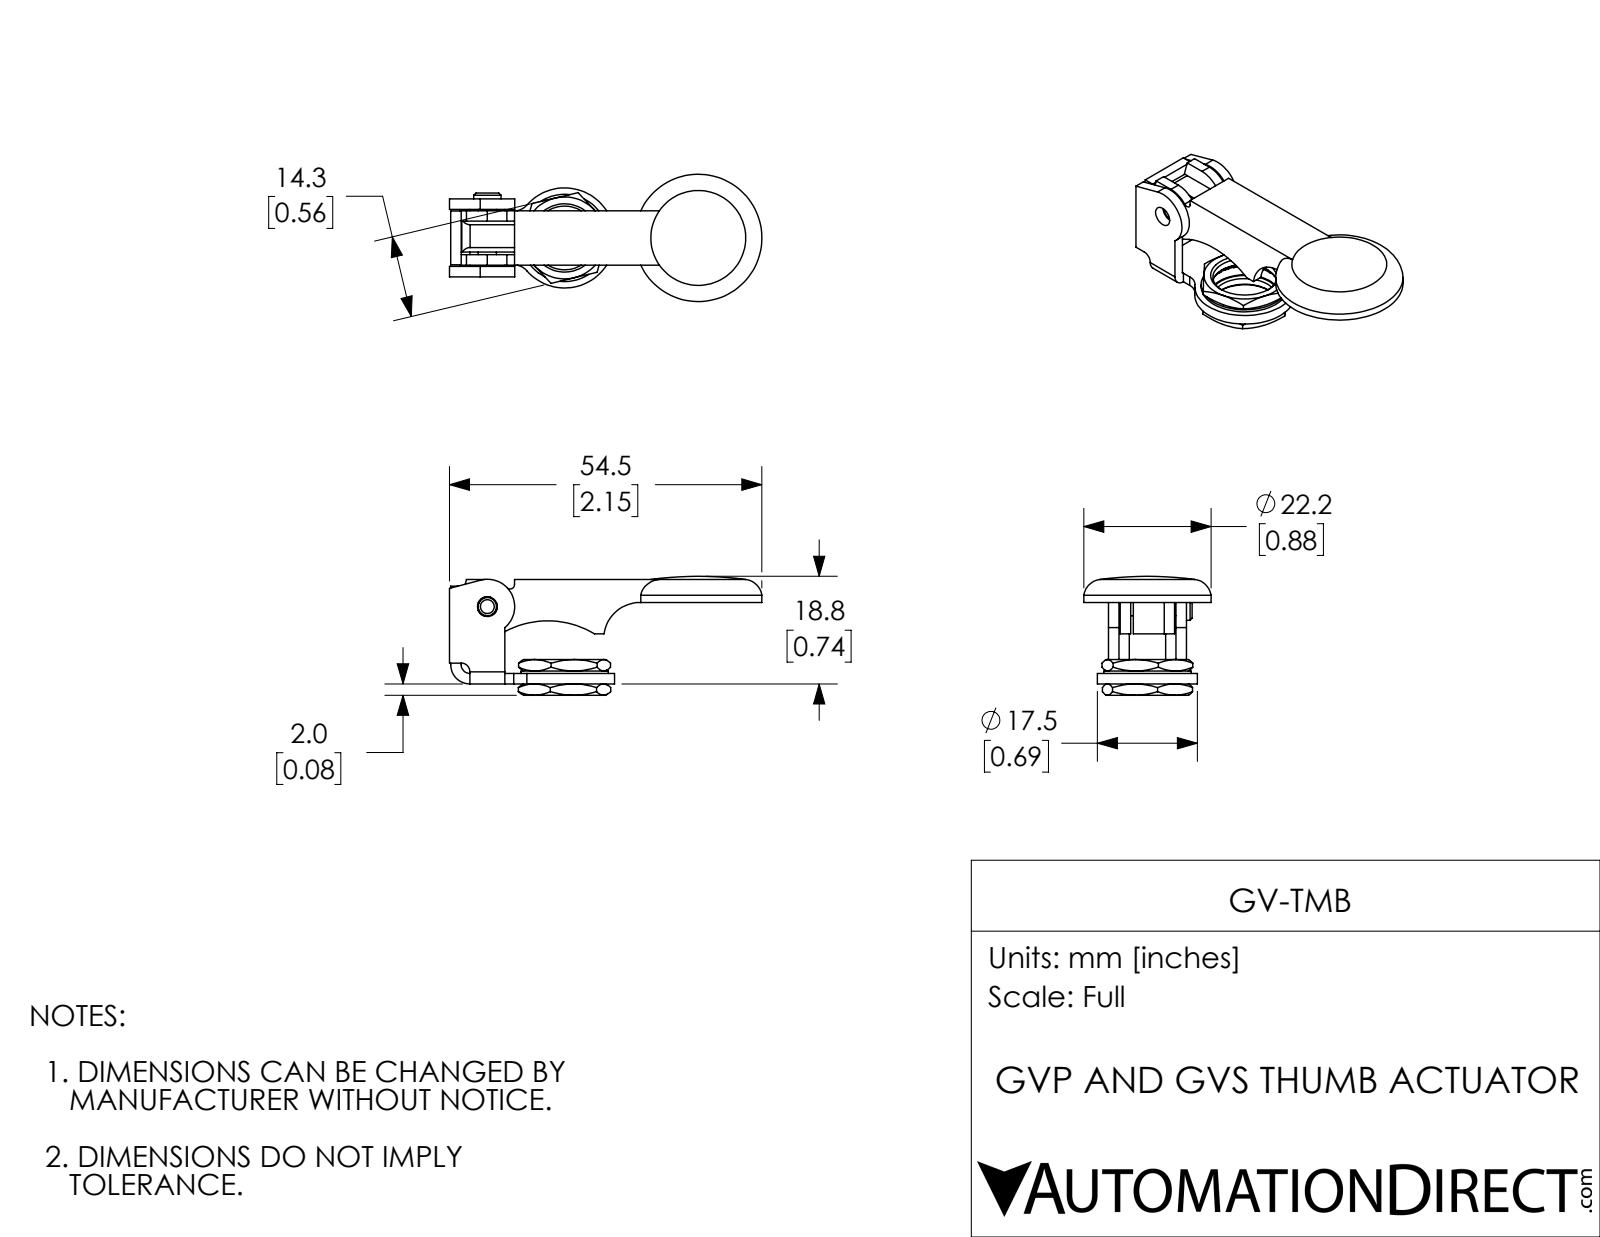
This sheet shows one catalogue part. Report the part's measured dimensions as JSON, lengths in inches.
{"part_name": "GV-TMB", "step_written_by": "SolidWorks 2018 (AUTOMOTIVE_DESIGN)", "units": "inches", "bodies": {"solids": 8, "faces": 304, "planar": 128, "cylindrical": 128, "other": 48}, "overall_size": [2.148, 0.875, 0.817], "volume_in3": 0.259, "surface_area_in2": 8.948, "round_holes": [[0.133, 1], [0.136, 1], [0.438, 1], [0.484, 1], [0.731, 1]], "round_bosses_or_shafts": [[0.875, 1], [0.6, 1], [0.187, 1], [0.125, 1], [0.125, 1], [0.096, 1]], "partial_cylinders_radius": [[0.06, 5], [0.014, 4], [0.011, 2], [0.018, 2], [0.083, 2], [0.12, 2], [0.031, 1], [0.047, 1]], "face_to_face_distances": [0.072, 0.081, 0.383, 0.302, 0.646, 0.153, 0.455, 0.464, 0.311, 0.374], "hole_center_spacings": [0.919]}
